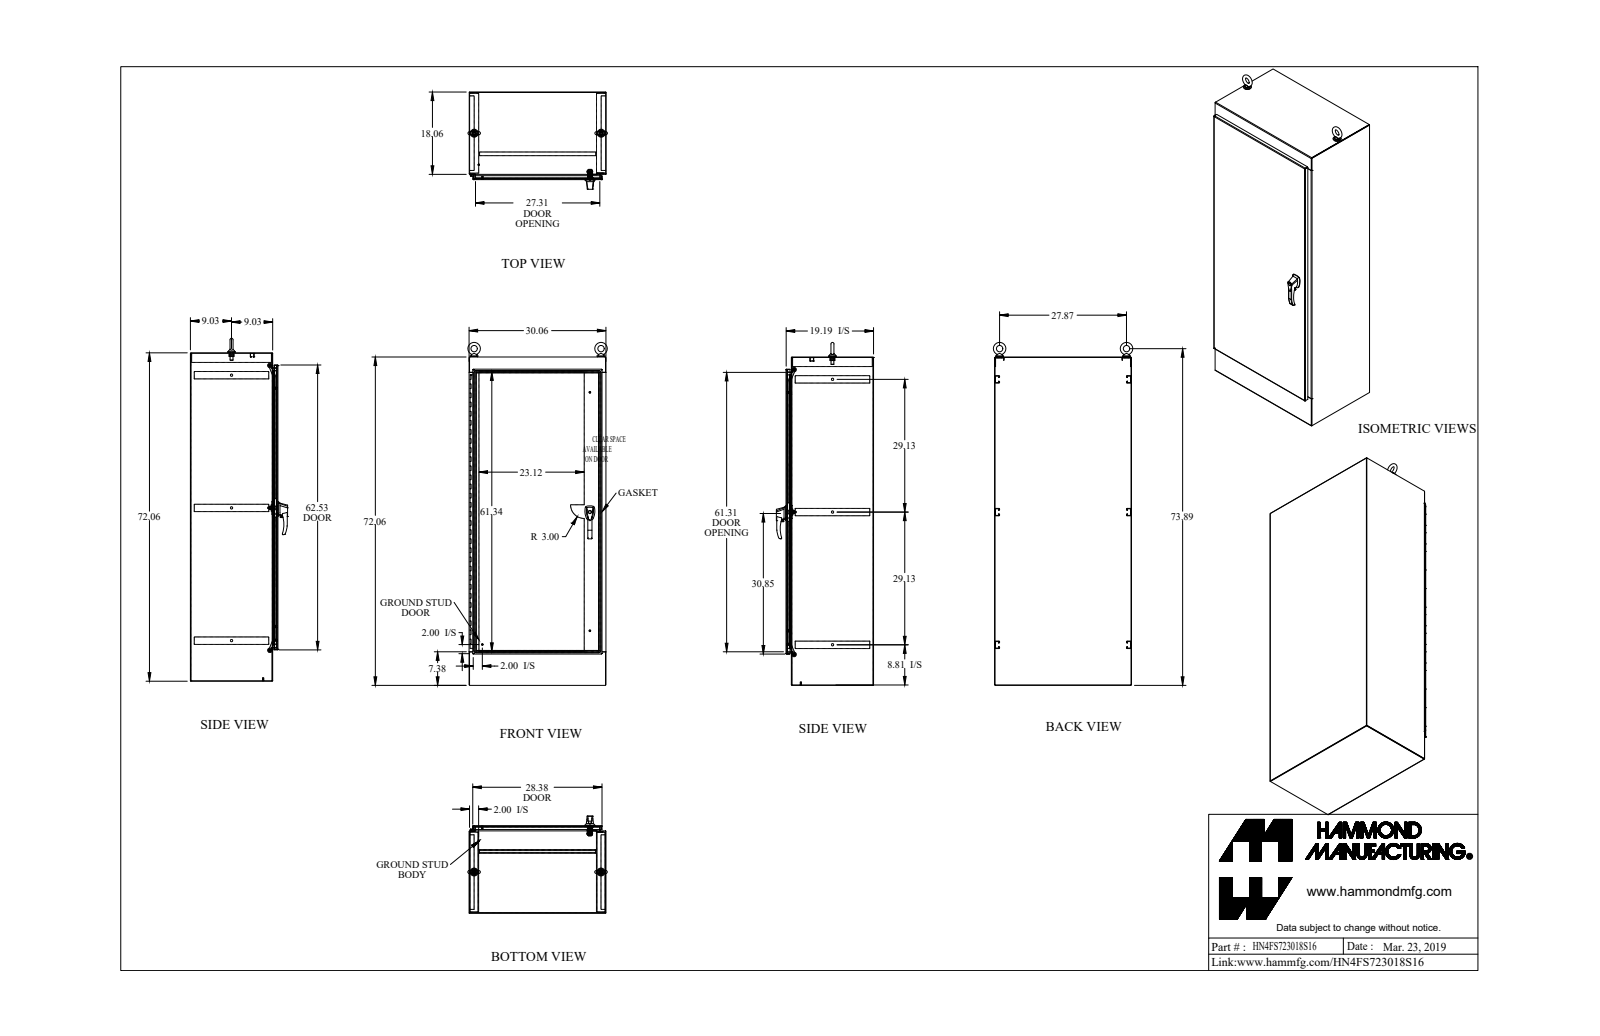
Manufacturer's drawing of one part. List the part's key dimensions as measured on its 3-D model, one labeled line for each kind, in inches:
Part name (STEP PRODUCT): HN4FS723018S16
STEP written by: SolidWorks 2018 (AUTOMOTIVE_DESIGN)
Units: inches
Bodies: 56 solids, 1875 faces (862 planar, 848 cylindrical, 165 other)
Overall size (bounding box): 75.256 × 30.604 × 21.337
Volume: 930.3 in³ · Surface area: 19 561 in²
Round holes (diameter × count): ⌀0.304 ×10, ⌀0.35 ×7, ⌀0.5 ×3, ⌀0.25 ×2, ⌀0.257 ×2, ⌀0.28 ×2, ⌀0.281 ×2, ⌀0.313 ×2, ⌀0.39 ×2, ⌀0.413 ×2, ⌀0.527 ×2, ⌀0.68 ×2
Round bosses / shafts (diameter × count): ⌀1.75 ×2, ⌀1.5 ×2, ⌀1.25 ×2, ⌀1 ×2, ⌀0.75 ×2, ⌀0.738 ×2, ⌀0.63 ×2, ⌀0.625 ×2
Partial cylindrical surfaces — rounded edges, fillets, slot ends (radius × count): R0.043 ×42, R0.138 ×36, R0.5 ×23, R0.125 ×22, R0.018 ×16, R0.06 ×15, R0.048 ×13, R0.143 ×13
Main face-to-face distances: 0.095, 19.127, 29.965, 19.032, 19.222, 29.87, 30.06, 71.965, 17.965, 1.162
Hole centre spacings: 6, 12, 18, 24, 30, 36, 42, 1.126
